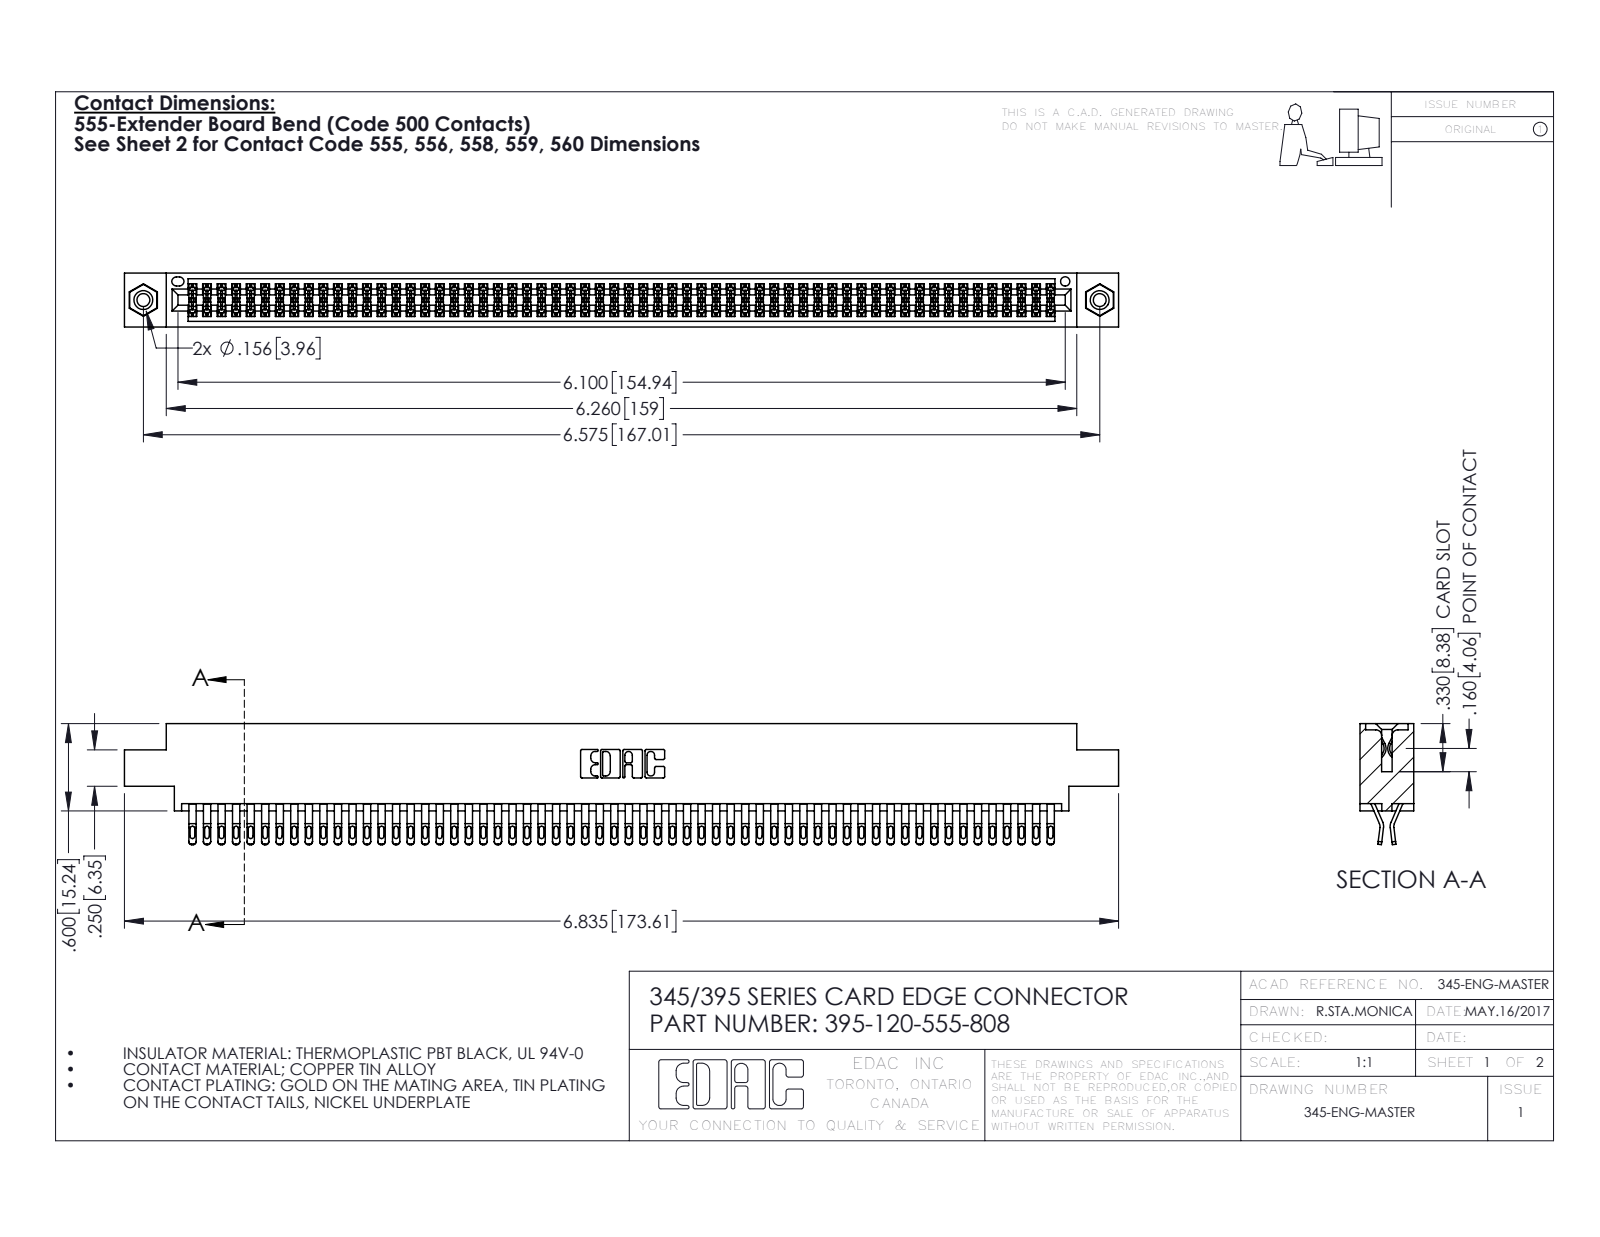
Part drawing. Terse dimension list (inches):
name: 345-292-001_555 Tail; 345-250-001_345-250-003-102; 395-120-555-808; 345 Part_0.170 Offset - 0.156 Dia-TI
written by: SolidWorks 2016 (CONFIG_CONTROL_DESIGN)
unit: in
bodies: 123 solids, 6910 faces (3836 planar, 3058 cylindrical, 16 other)
size: 6.835 × 0.832 × 0.37
volume: 1.053 in³; area: 42.21 in²
holes: 2× ⌀0.089, 2× ⌀0.125, 2× ⌀0.156, 1× ⌀0.064
bosses: 2× ⌀0.155
rounds: 300× R0.016, 240× R0.02, 180× R0.006, 22× R0.01, 6× R0.007, 6× R0.031, 3× R0.026, 2× R0.01
face distances: 0.072, 0.298, 0.025, 0.37, 0.2, 0.098, 0.272, 0.225, 0.175, 0.149
hole spacings: 0.27, 6.339, 6.575
